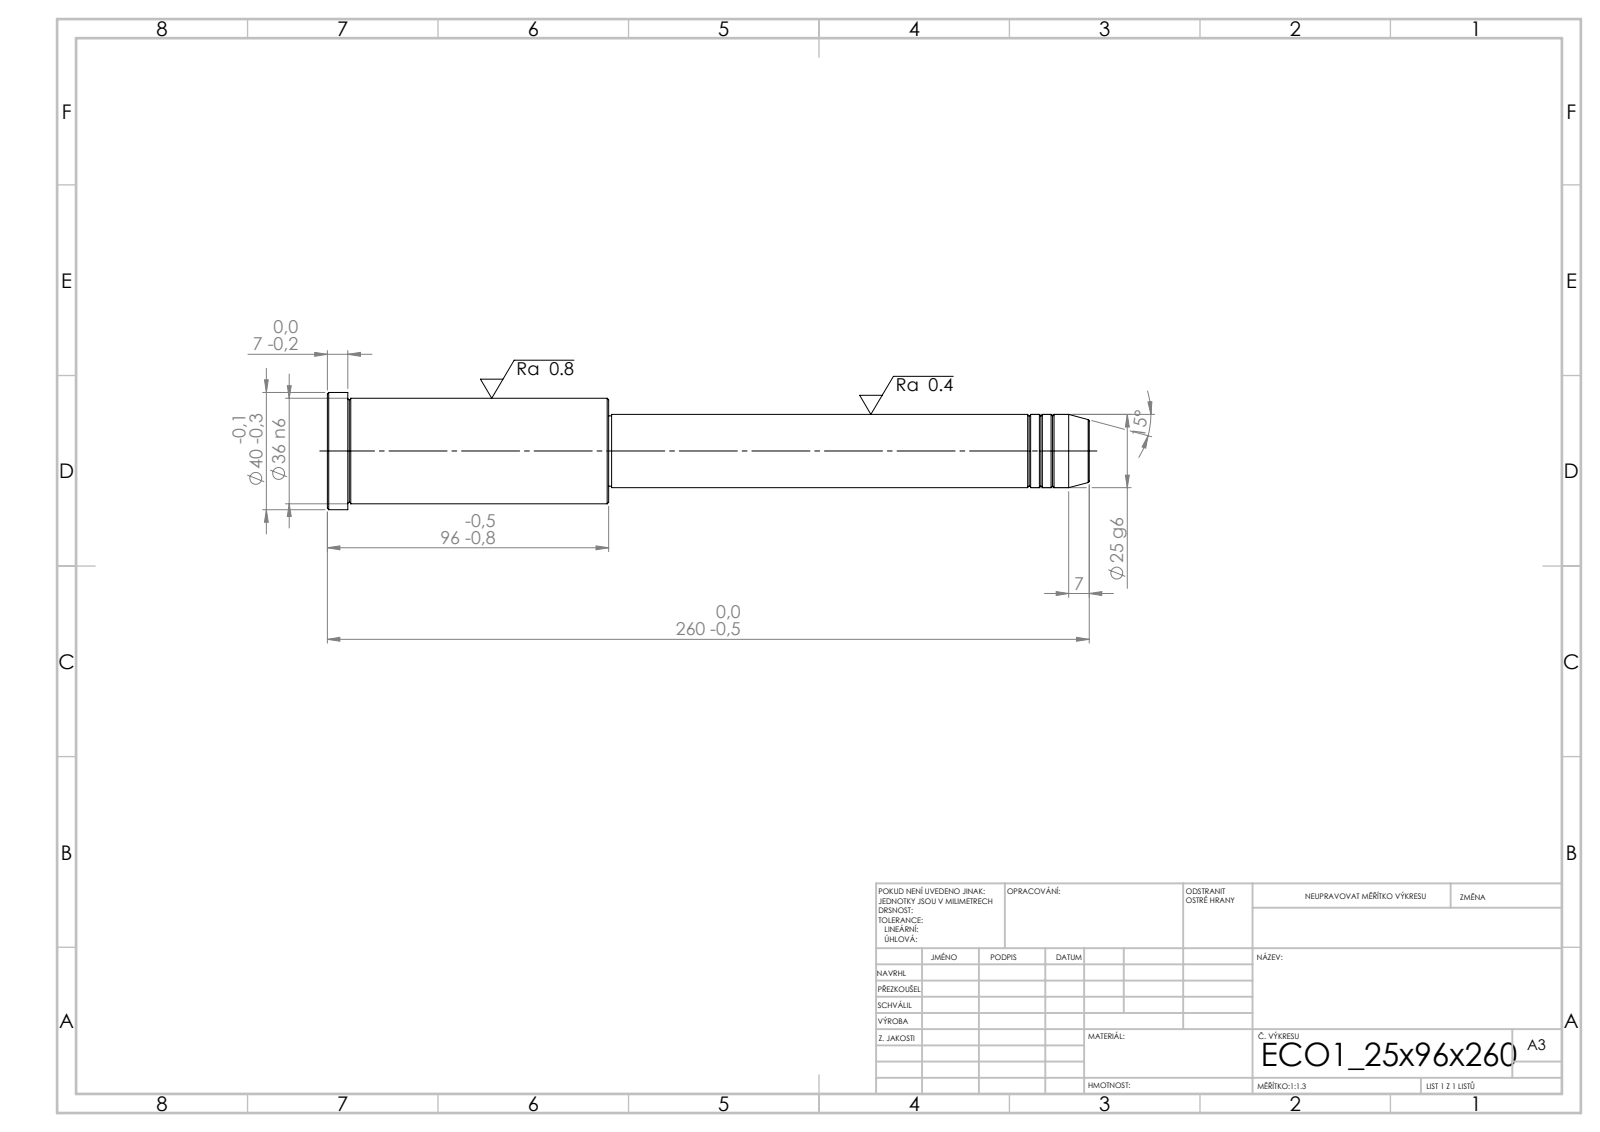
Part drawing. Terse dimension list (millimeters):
written by: SolidWorks 2019 (CONFIG_CONTROL_DESIGN)
unit: mm
bodies: 1 solid, 43 faces (5 planar, 14 cylindrical, 24 other)
size: 260 × 40 × 40
volume: 179 196 mm³; area: 26 362 mm²
bosses: 1× ⌀40, 1× ⌀36, 1× ⌀25, 1× ⌀24
face distances: 96, 164, 260, 253, 89, 7, 163, 1, 90, 97
